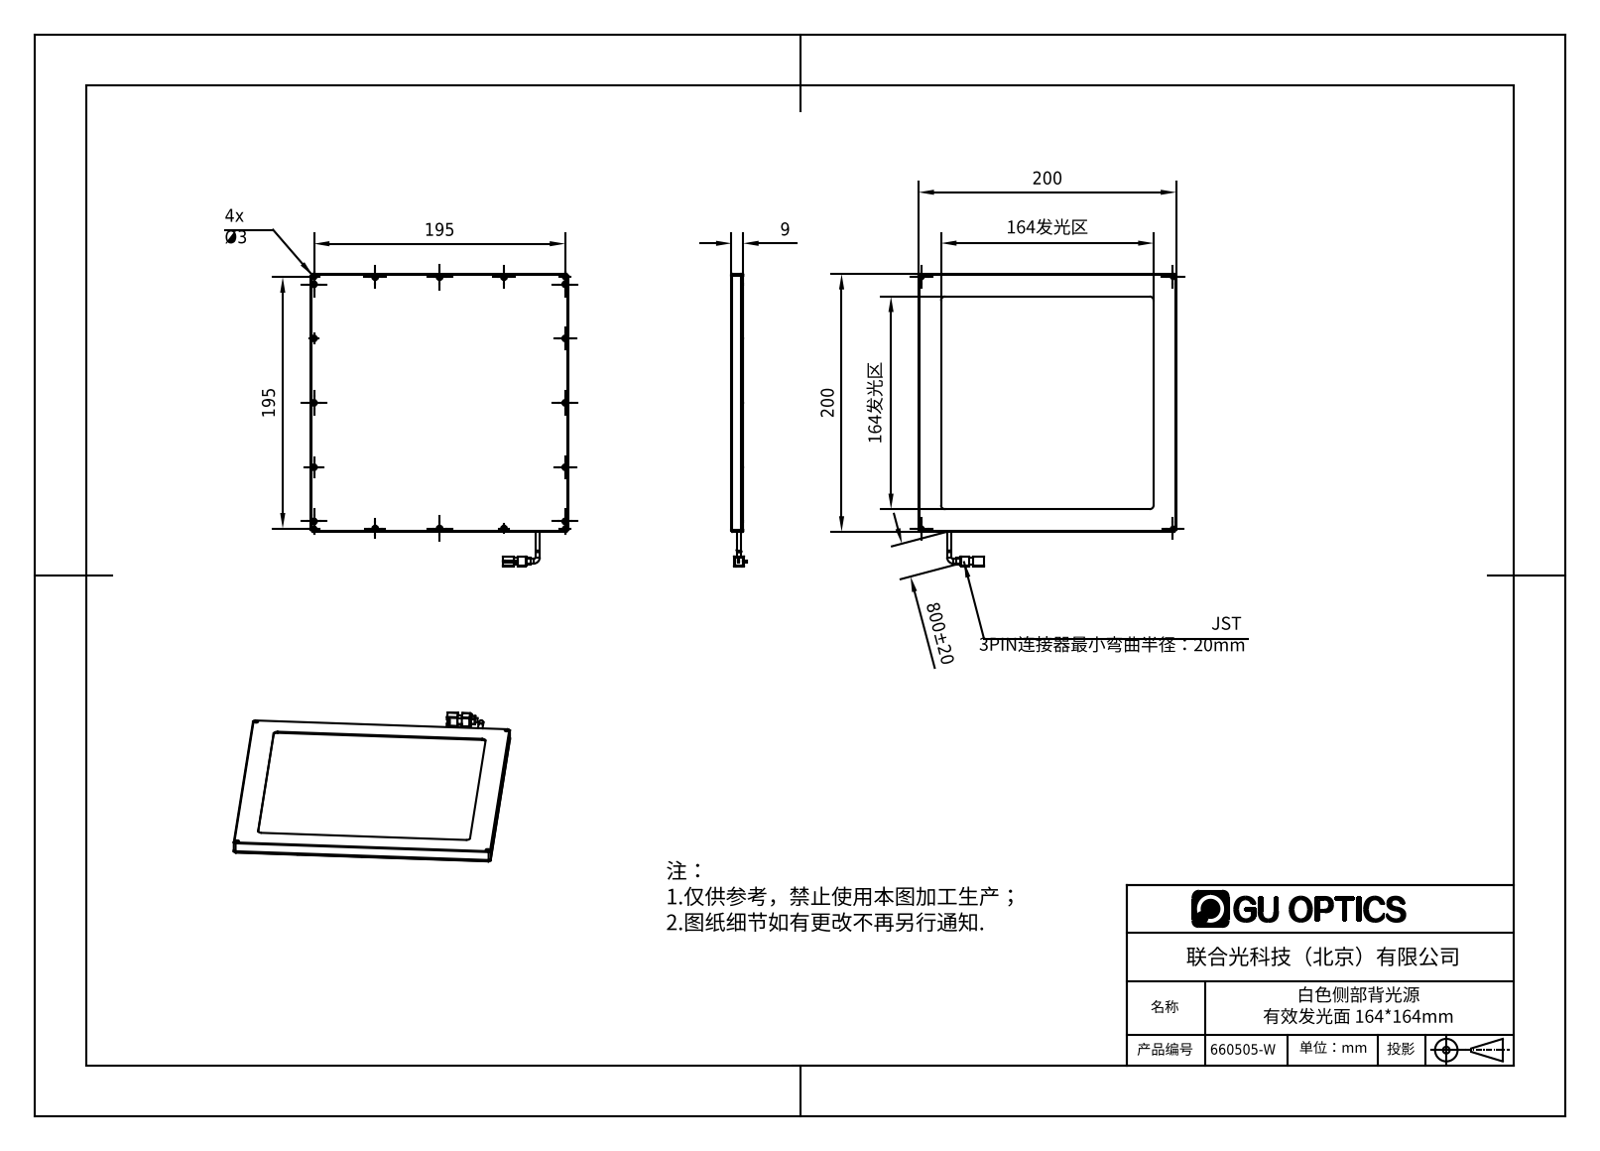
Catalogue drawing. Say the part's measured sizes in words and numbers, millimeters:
The part is named "660505-W". Its 3-D file was written by "SolidWorks 2016 (AUTOMOTIVE_DESIGN)". It is 7 solids with 732 faces: 472 planar, 134 cylindrical and 126 other. Overall it measures 227 by 200 by 11.8 millimeters. Its volume is 224 961 cubic millimeters and its surface area 192 480 square millimeters. Round holes: 16 of diameter 1.6, 16 of diameter 2.4, 8 of diameter 2, 4 of diameter 3, 4 of diameter 3.3. Round bosses or shafts: 2 of diameter 3.5. Partial cylindrical surfaces (rounded edges, fillets, slot ends): 8 of radius 0.5, 8 of radius 3, 6 of radius 1.5, 4 of radius 1, 1 of radius 1.6. The main face-to-face distances are 4, 6.5, 8, 1.5, 2.5, 7.5, 1, 5, 9, 196. The hole center spacings are 195, 47.5, 50, 97.5, 108.46, 147.5, 154.96, 176.81.
